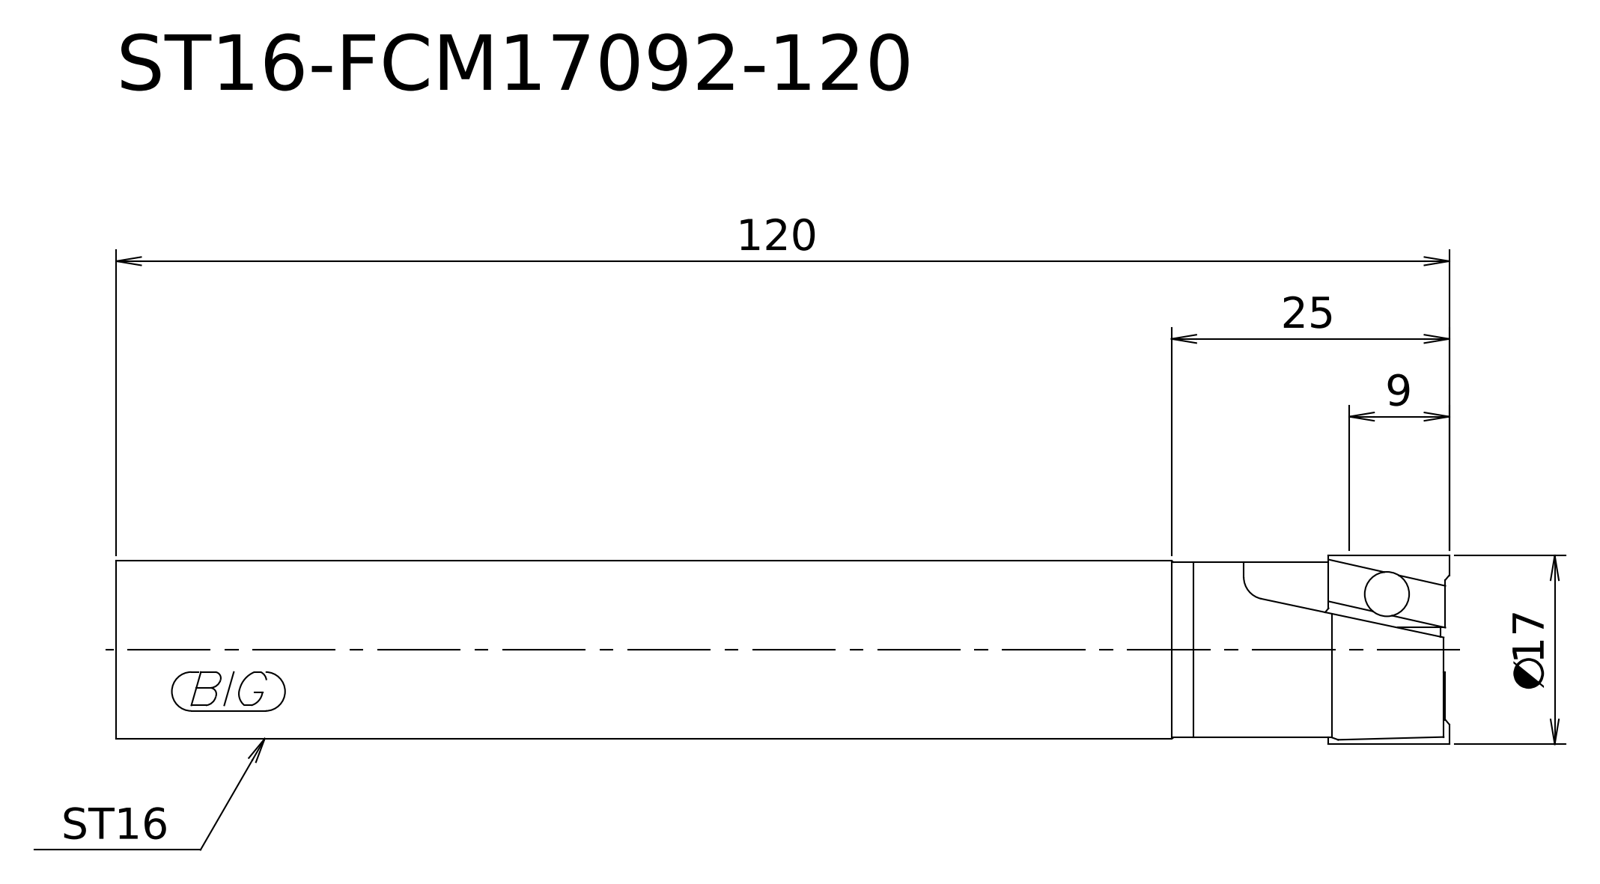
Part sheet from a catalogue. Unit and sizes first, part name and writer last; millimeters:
Units: millimetres
Overall size (bounding box): 120 × 17 × 17
Round bosses / shafts (diameter × count): ⌀17 ×1, ⌀16 ×1, ⌀15.8 ×1
Main face-to-face distances: 120, 10.86, 109.14
Volume: 24 339 mm³ · Surface area: 6 517 mm²
Bodies: 1 solid, 7 faces (3 planar, 3 cylindrical, 1 other)
STEP written by: Kubotek KeyCreator V8.5.1 (14335) (CONFIG_CONTROL_DESIGN)
